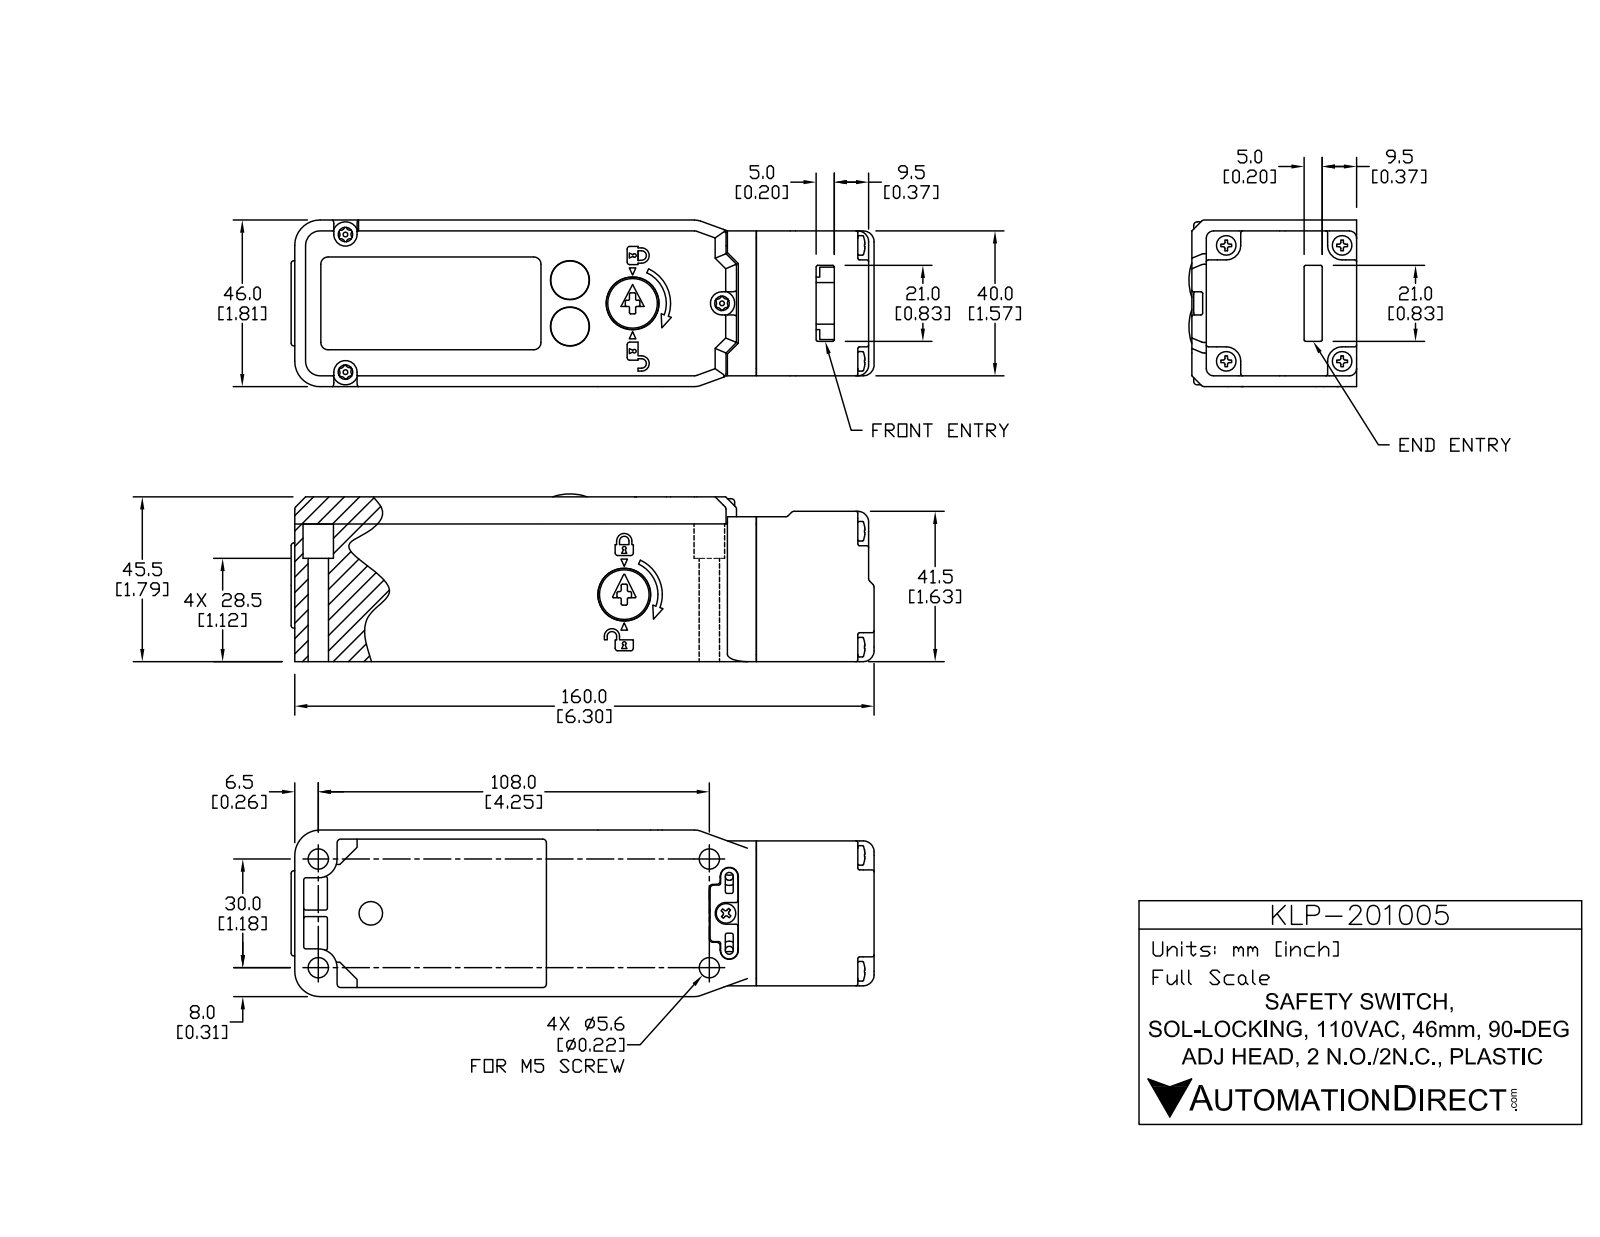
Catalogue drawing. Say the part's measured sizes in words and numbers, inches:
The part is named "KLP-201005". Its 3-D file was written by "SolidWorks 2017 (AUTOMOTIVE_DESIGN)". It is 8 solids with 476 faces: 172 planar, 208 cylindrical and 96 other. Overall it measures 6.339 by 1.823 by 1.811 inches. Its volume is 18.35 cubic inches and its surface area 79.89 square inches. Round holes: 4 of diameter 0.209, 4 of diameter 0.386, 2 of diameter 0.425, 1 of diameter 0.276. Round bosses or shafts: 4 of diameter 0.213, 3 of diameter 0.051, 2 of diameter 0.276, 1 of diameter 0.925. Partial cylindrical surfaces (rounded edges, fillets, slot ends): 65 of radius 0.02, 21 of radius 0.039, 11 of radius 0.079, 4 of radius 0.118, 4 of radius 0.157, 3 of radius 0.098, 2 of radius 0.045, 2 of radius 0.197. The main face-to-face distances are 1.496, 1.811, 1.791, 0.295, 0.118, 1.693, 1.575, 0.374, 5.019, 5.02. The hole center spacings are 1.181, 1.553, 1.734, 2.757, 2.863, 4.252, 4.413, 0.335.
